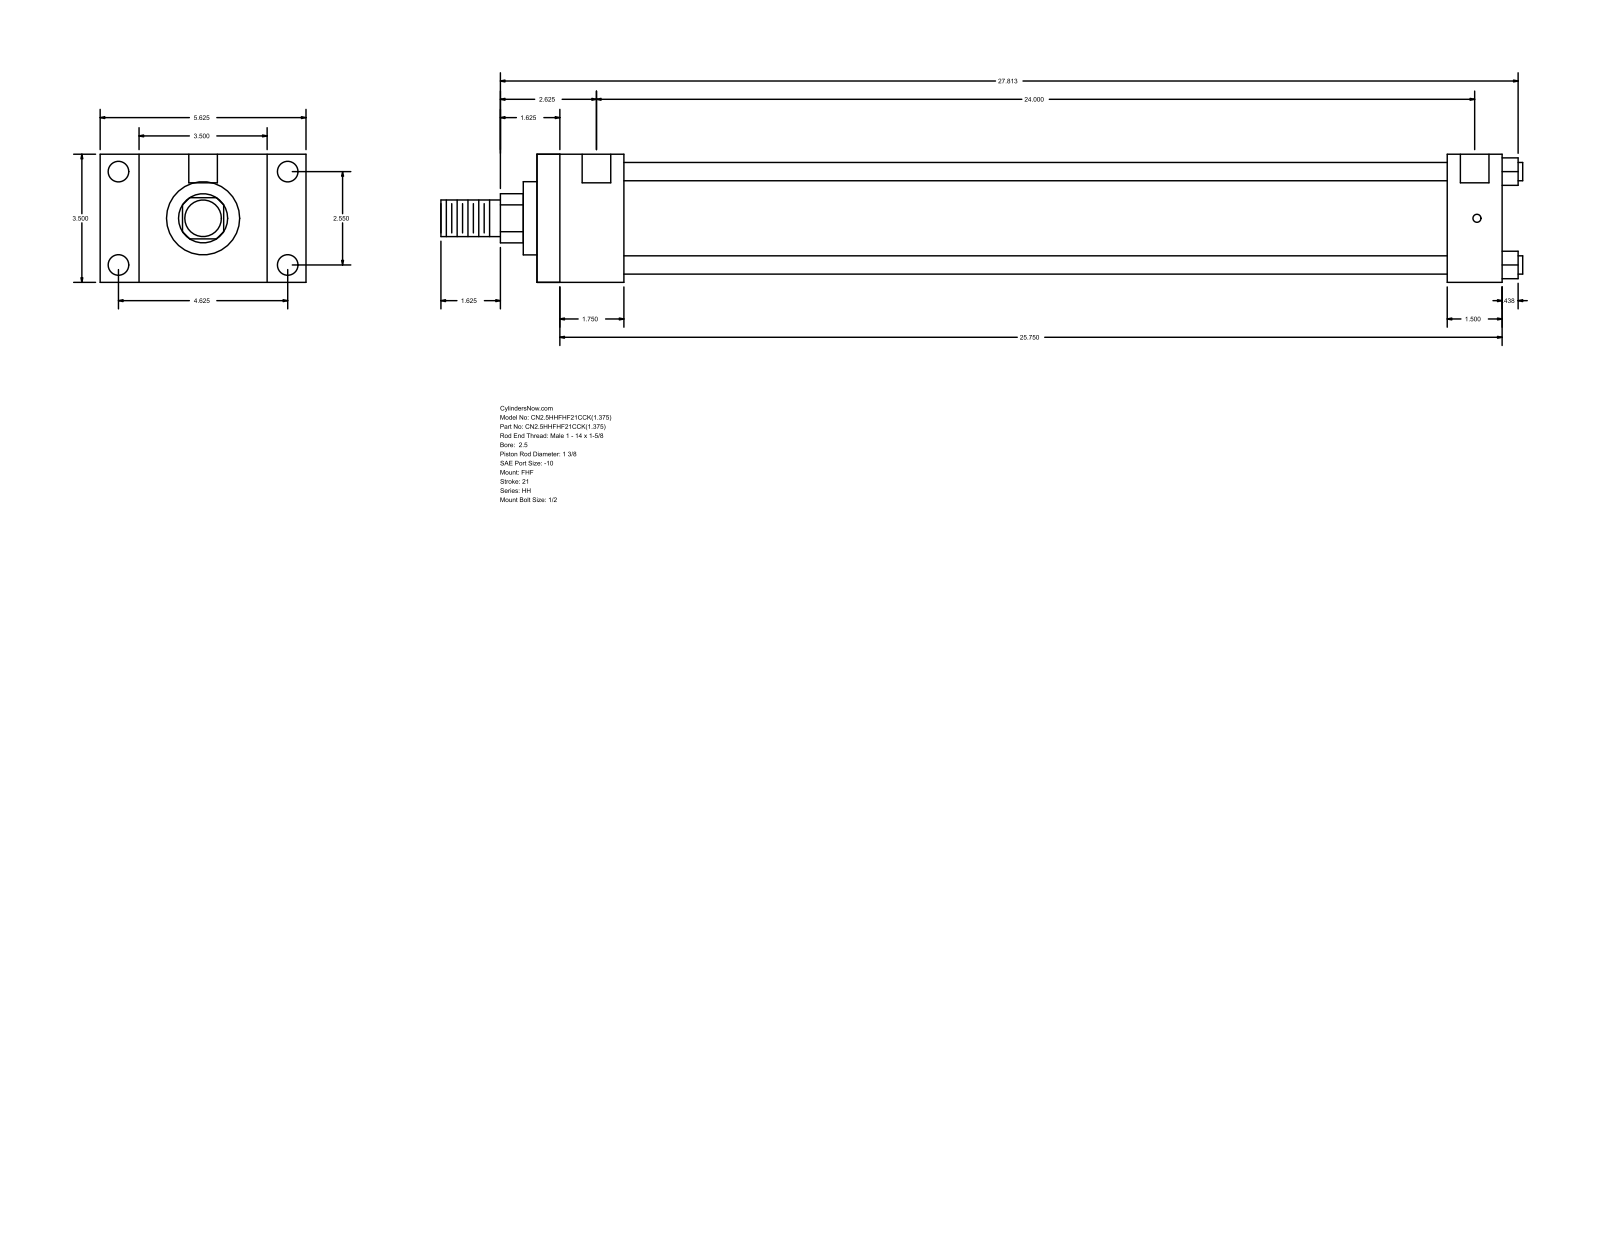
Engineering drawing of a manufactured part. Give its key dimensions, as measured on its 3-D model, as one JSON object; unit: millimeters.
{"part_name": "HH_FHF__0250_1.375", "step_written_by": "GSSL Pune (CONFIG_CONTROL_DESIGN)", "units": "millimeters", "bodies": {"solids": 0, "faces": 88, "planar": 60, "cylindrical": 28, "other": 0}, "overall_size": [750.89, 142.88, 88.9], "round_holes": [[5.56, 4], [14.3, 4], [19.84, 2]], "round_bosses_or_shafts": [[12.7, 4], [73.03, 1], [50.8, 1], [34.92, 1], [25.4, 1]], "partial_cylinders_radius": [[17.06, 1]], "face_to_face_distances": [88.9, 60.32, 26.99, 115.89, 669.93, 609.61, 142.88, 631.83, 571.51, 38.1], "hole_center_spacings": [64.76, 117.48, 134.15, 612.77, 1.58, 1.59, 609.6, 611.18]}
